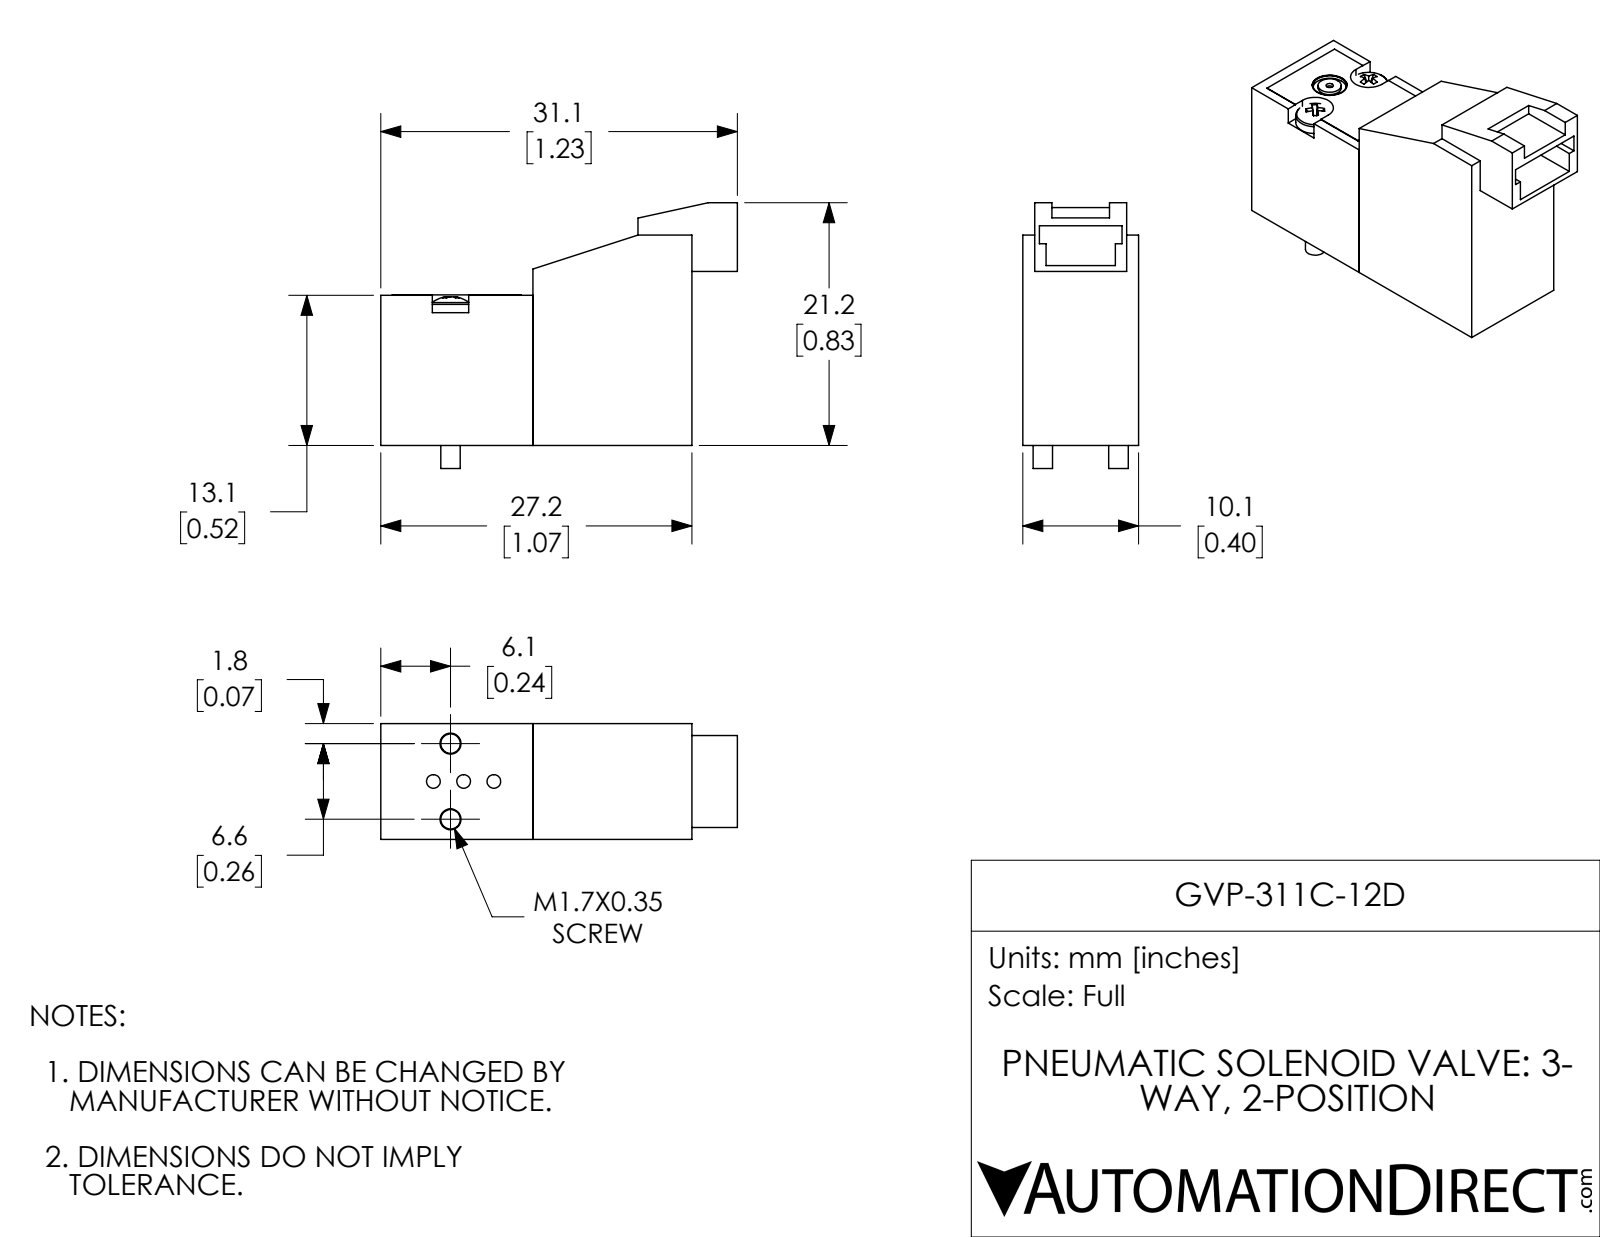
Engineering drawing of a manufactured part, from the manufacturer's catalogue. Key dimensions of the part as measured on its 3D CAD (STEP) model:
Part name (STEP PRODUCT): GVP-311C-12D
STEP written by: SolidWorks 2018 (AUTOMOTIVE_DESIGN)
Units: inches
Bodies: 4 solids, 126 faces (83 planar, 29 cylindrical, 14 other)
Overall size (bounding box): 1.226 × 0.913 × 0.398
Volume: 0.259 in³ · Surface area: 4.199 in²
Round holes (diameter × count): ⌀0.047 ×3, ⌀0.072 ×2, ⌀0.025 ×1, ⌀0.115 ×1, ⌀0.12 ×1
Round bosses / shafts (diameter × count): ⌀0.134 ×2, ⌀0.067 ×2, ⌀0.08 ×1
Partial cylindrical surfaces — rounded edges, fillets, slot ends (radius × count): R0.062 ×2
Main face-to-face distances: 0.398, 0.547, 1.07, 0.523, 0.517, 0.238, 0.041, 0.357, 0.755, 0.618
Hole centre spacings: 0.104, 0.198, 0.105, 0.137, 0.138, 0.143, 0.143, 0.143
